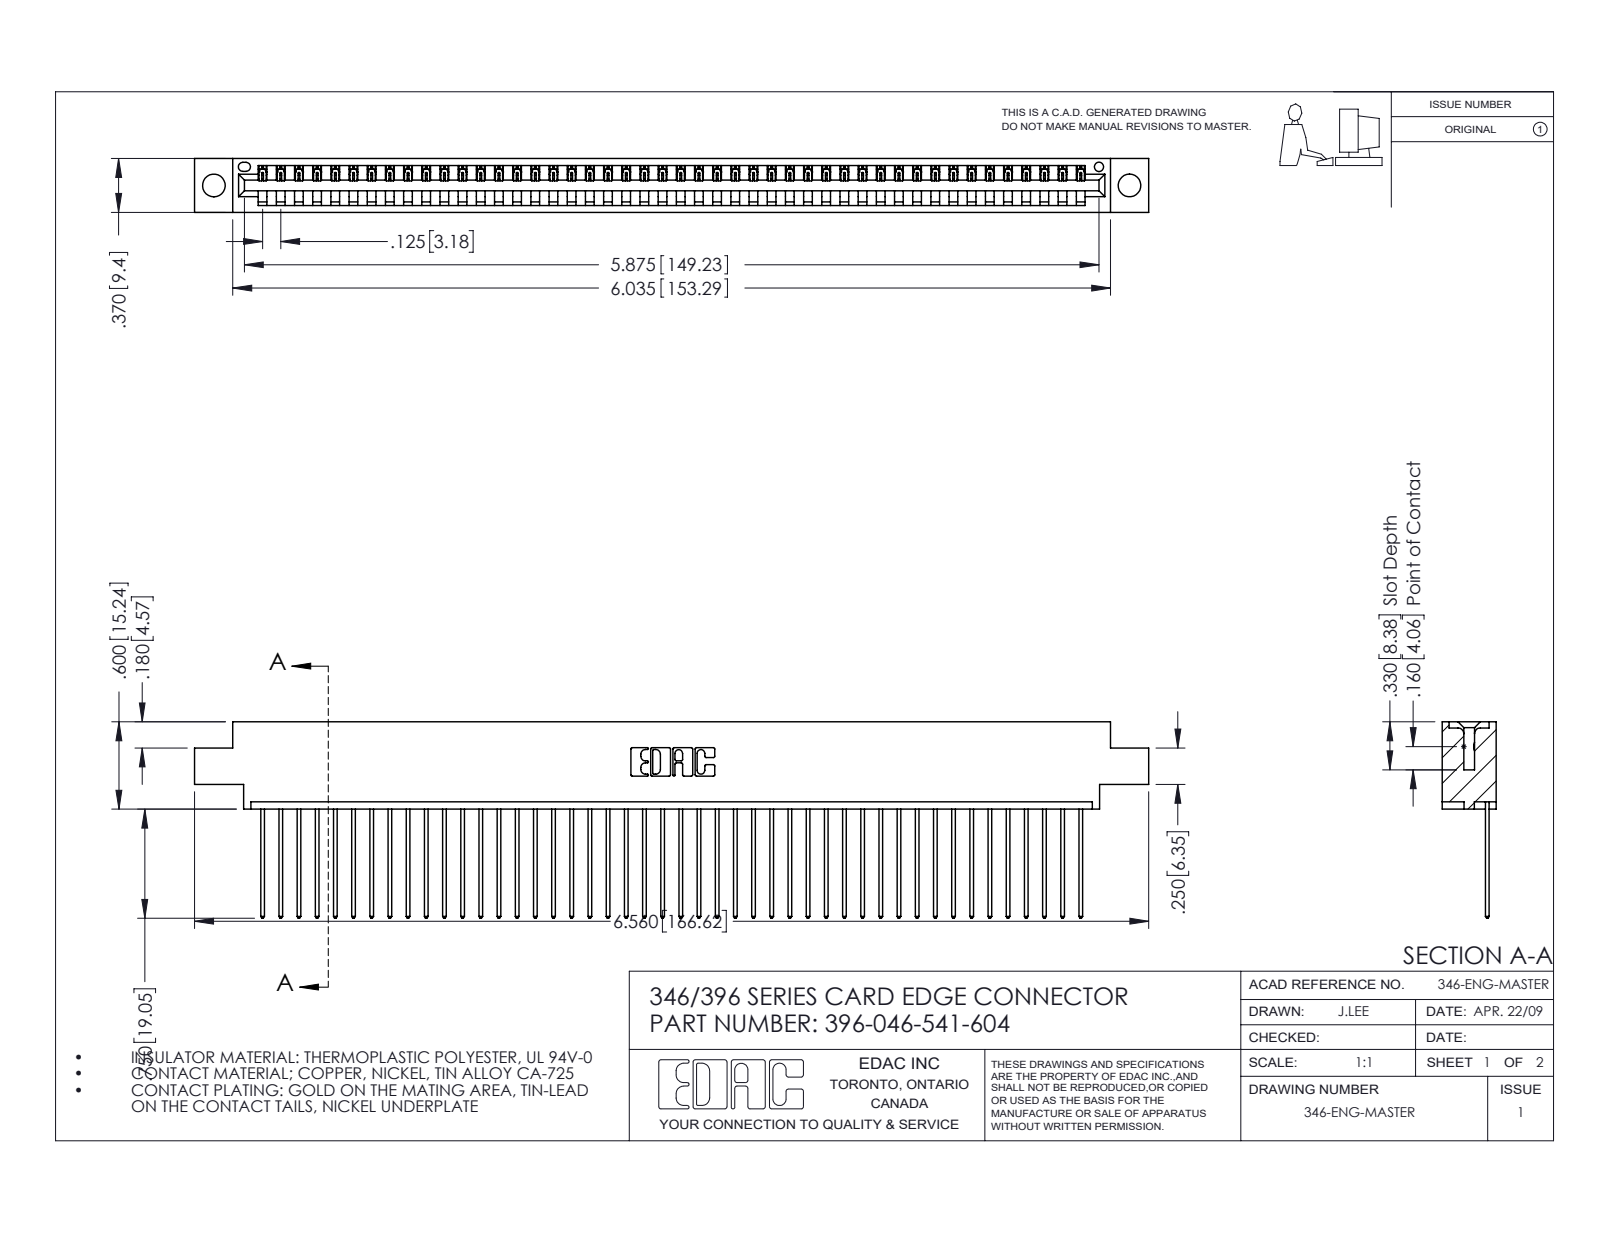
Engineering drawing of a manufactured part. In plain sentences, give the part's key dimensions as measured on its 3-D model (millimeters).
The part is named "396-046-541-604; 346 Part_0.170 Offset - 0.156 Dia-TH; 345-292-001_345-293-141". Its 3-D file was written by "SolidWorks 2016 (CONFIG_CONTROL_DESIGN)". It is 47 solids with 2794 faces: 1920 planar, 874 cylindrical and 0 other. Overall it measures 166.6 by 34.3 by 9.4 millimeters. Its volume is 15 900 cubic millimeters and its surface area 20 770 square millimeters. Round holes: 2 of diameter 4, 1 of diameter 1.6. Partial cylindrical surfaces (rounded edges, fillets, slot ends): 92 of radius 0.2, 92 of radius 0.3, 22 of radius 0.3, 6 of radius 0.2, 6 of radius 0.8, 3 of radius 0.7, 2 of radius 0.8, 2 of radius 1. The main face-to-face distances are 1.2, 8.2, 9.4, 6.4, 1.8, 7.6, 0.6, 3.8, 5.6, 2.5. The hole center spacings are 6.2, 154.6, 159.9.
